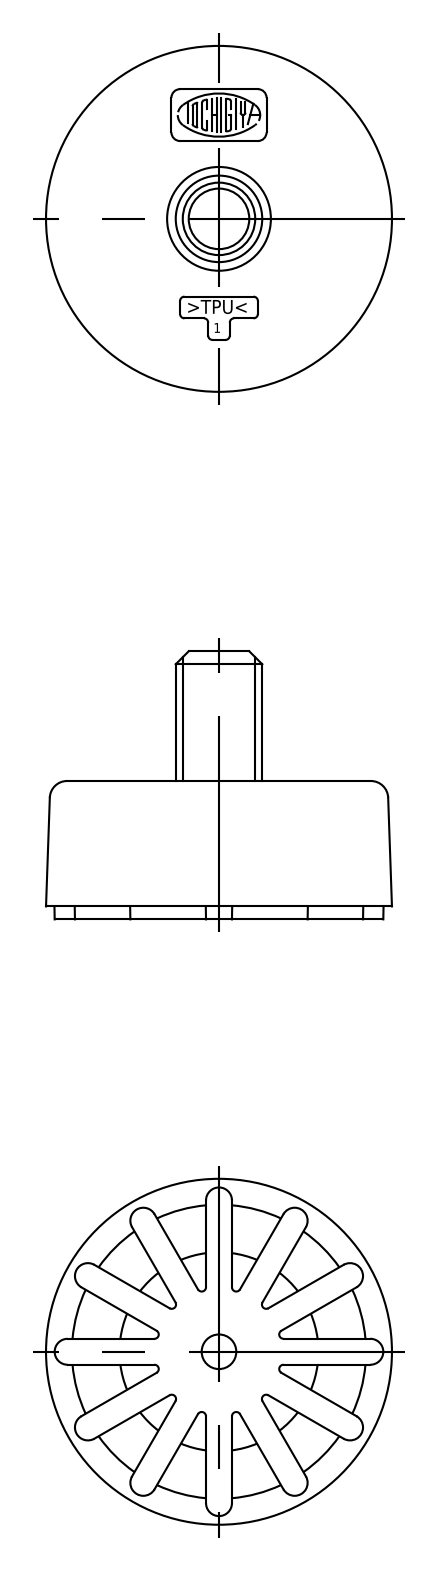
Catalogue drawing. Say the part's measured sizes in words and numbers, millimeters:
Its 3-D file was written by "spGate 19.8.4 (****-****-****-****) (AUTOMOTIVE_DESIGN)". It is 1 solid with 161 faces: 101 planar, 28 cylindrical and 32 other. Overall it measures 40 by 40 by 31 millimeters. Its volume is 17 468 cubic millimeters and its surface area 7 130 square millimeters. Round holes: 1 of diameter 12. Round bosses or shafts: 1 of diameter 10. Partial cylindrical surfaces (rounded edges, fillets, slot ends): 12 of radius 0.5, 12 of radius 1.5. The main face-to-face distances are 16, 1.5, 14.5, 9, 7.5, 7, 31, 29.5, 22, 15.
